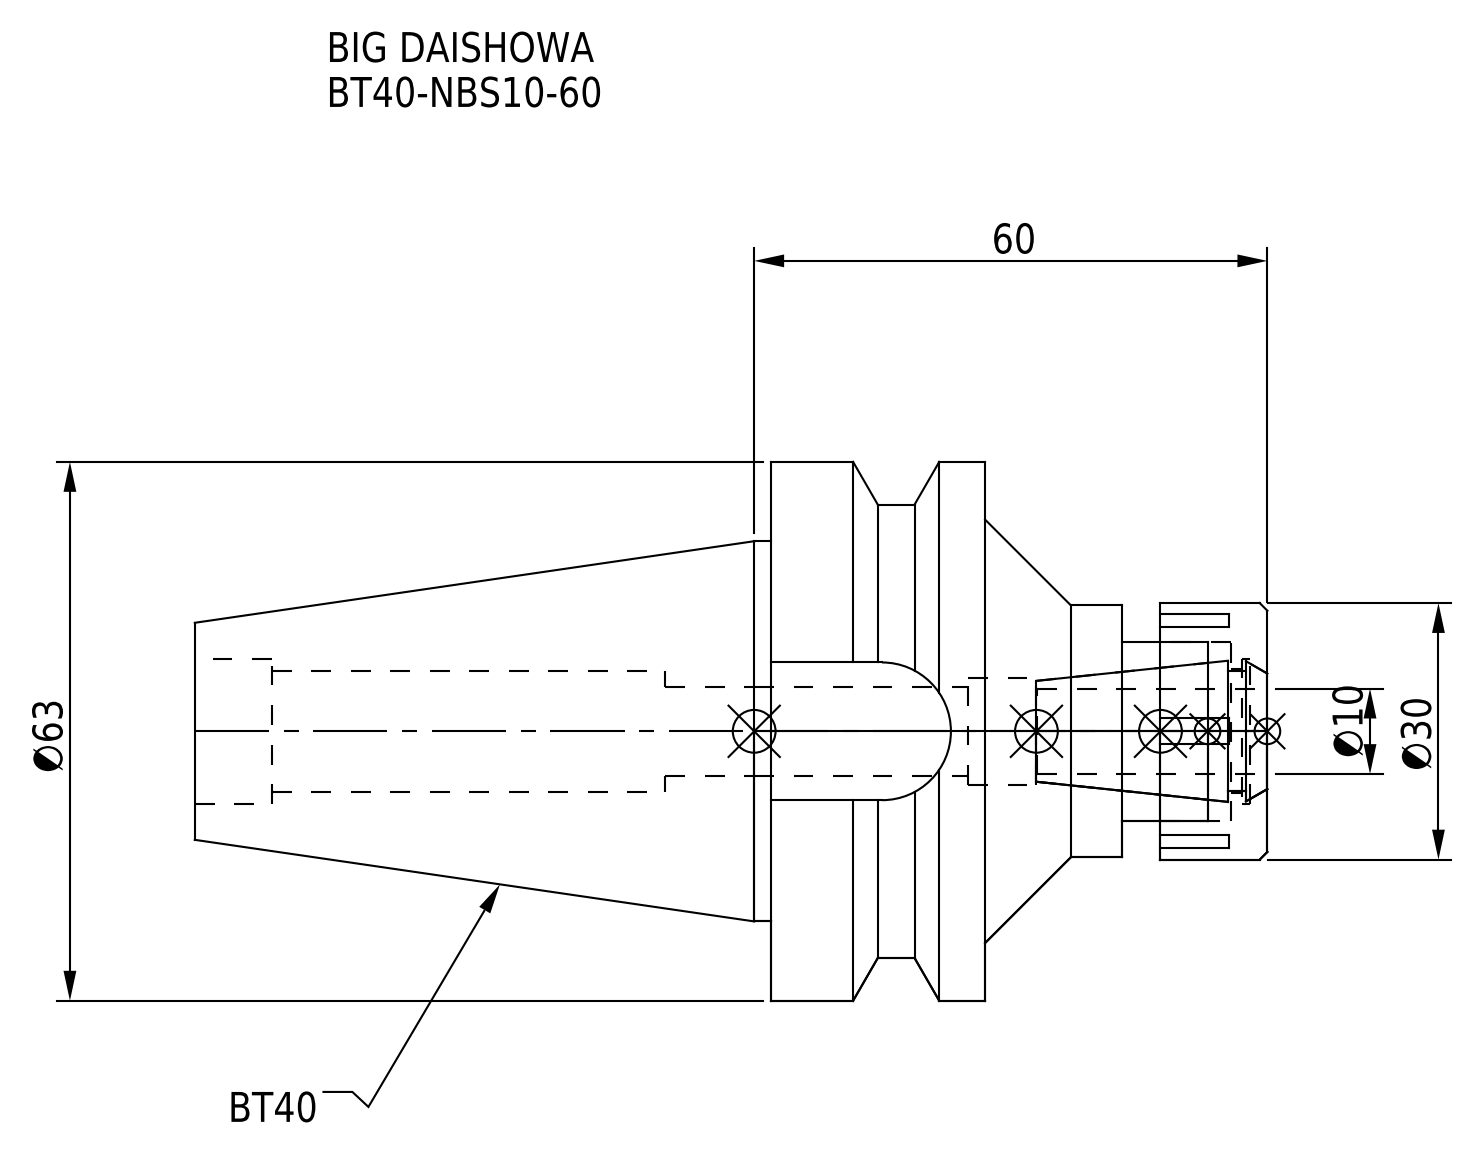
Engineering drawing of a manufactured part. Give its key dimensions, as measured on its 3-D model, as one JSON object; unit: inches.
{"part_name": "BT40-NBS10-60; BT40-NBS10-60.stp; DXF_TEMP_ASSY_ASM_4_ASM.stp; BT40-NBS10-60_1.stp (+3 more)", "step_written_by": "SolidWorks 2019 (CONFIG_CONTROL_DESIGN)", "units": "inches", "bodies": {"solids": 2, "faces": 90, "planar": 44, "cylindrical": 32, "other": 14}, "overall_size": [4.937, 2.48, 2.48], "volume_in3": 8.72, "surface_area_in2": 43.97, "round_holes": [[0.409, 1], [0.492, 1], [0.559, 1], [0.571, 1], [0.669, 1], [0.827, 1]], "round_bosses_or_shafts": [[2.48, 1], [2.087, 1], [1.75, 1], [1.181, 1], [1.161, 1]], "partial_cylinders_radius": [[0.317, 1]], "face_to_face_distances": [0.984, 1.299, 2.283, 0.177, 0.492, 2.654, 0.669, 0.63, 1.614, 0.807]}
